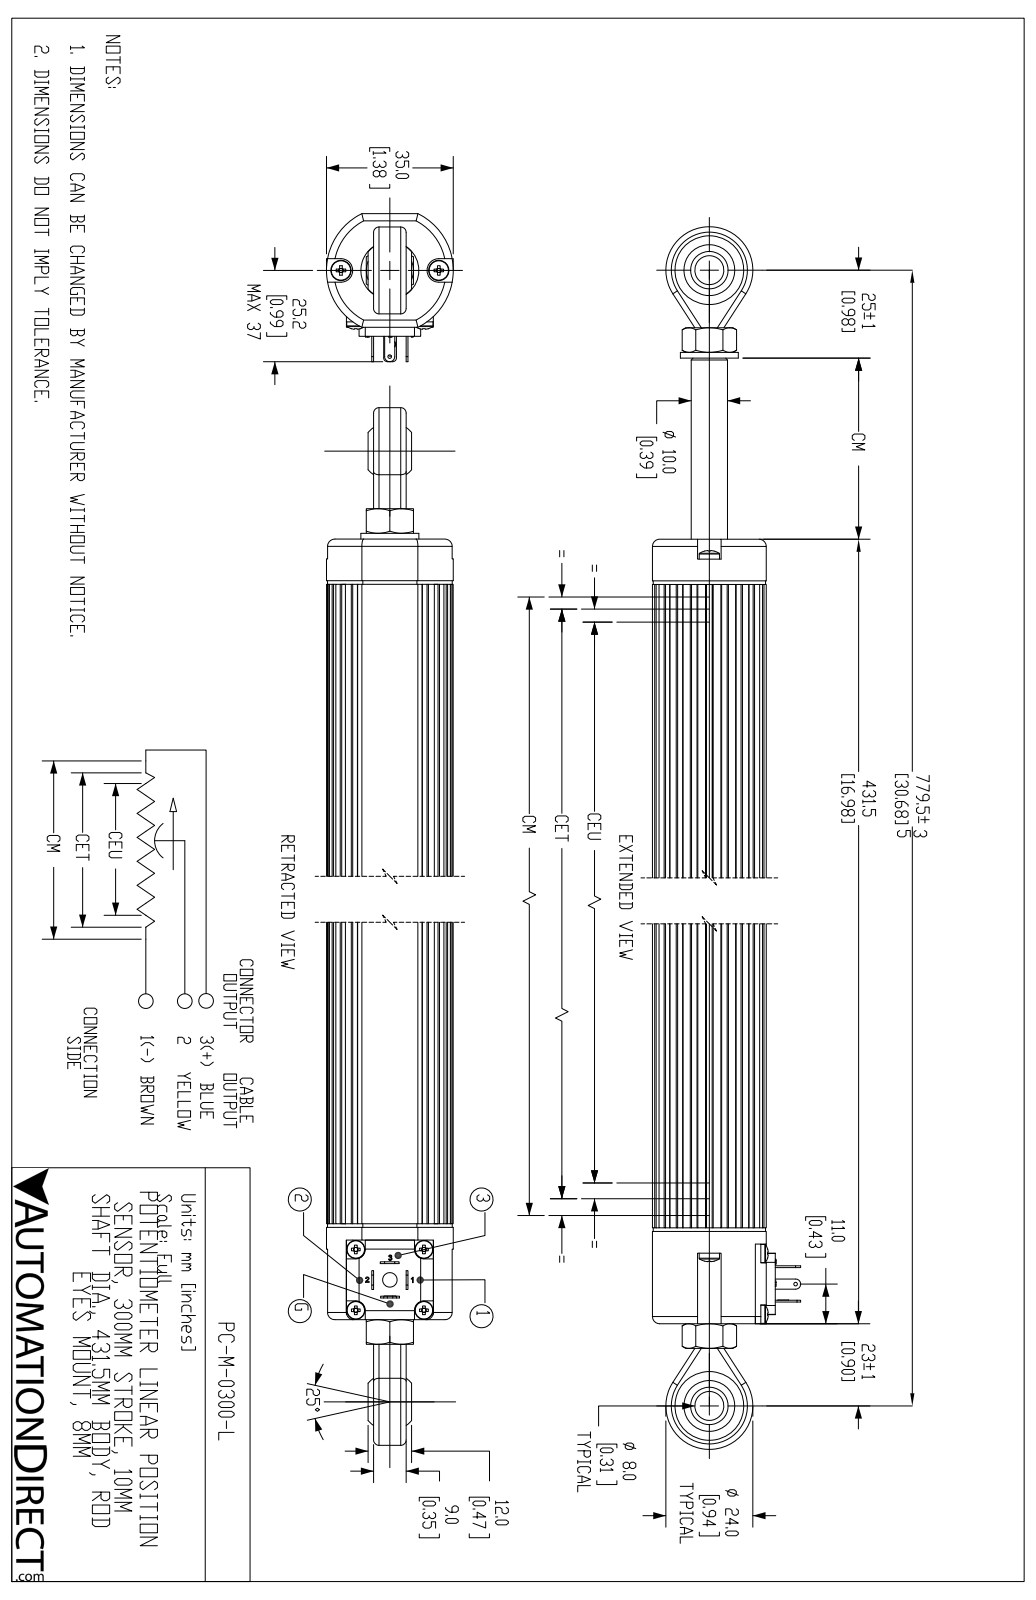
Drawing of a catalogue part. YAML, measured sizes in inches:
part_name: "PC-M-0300-L"
step_written_by: "SolidWorks 2019 (AUTOMOTIVE_DESIGN)"
units: inches
bodies: {solids: 26, faces: 1441, planar: 437, cylindrical: 366, other: 638}
overall_size: [20.025, 1.61, 1.378]
volume: 26.44
surface_area: 140.1
round_holes:
  - {diameter: 0.087, count: 4}
  - {diameter: 0.102, count: 4}
  - {diameter: 0.039, count: 3}
  - {diameter: 0.108, count: 2}
  - {diameter: 0.138, count: 2}
  - {diameter: 0.315, count: 2}
  - {diameter: 0.748, count: 2}
  - {diameter: 0.114, count: 1}
  - {diameter: 0.157, count: 1}
  - {diameter: 0.268, count: 1}
  - {diameter: 0.331, count: 1}
  - {diameter: 0.512, count: 1}
round_bosses_or_shafts:
  - {diameter: 0.197, count: 4}
  - {diameter: 0.098, count: 4}
  - {diameter: 0.118, count: 3}
  - {diameter: 0.22, count: 2}
  - {diameter: 0.63, count: 1}
  - {diameter: 0.394, count: 1}
  - {diameter: 0.39, count: 1}
  - {diameter: 0.315, count: 1}
partial_cylinders:
  - {radius: 0.059, count: 8}
  - {radius: 0.039, count: 5}
  - {radius: 0.079, count: 5}
  - {radius: 0.102, count: 4}
  - {radius: 0.118, count: 4}
  - {radius: 0.055, count: 2}
  - {radius: 0.128, count: 2}
  - {radius: 0.472, count: 2}
face_to_face_distances: [1.236, 0.039, 15.492, 0.913, 15.453, 0.913, 15.531, 0.118, 1.118, 16.535]
hole_center_spacings: [0.496, 0.531, 0.661, 0.74, 0.993, 0.024, 0.11, 0.134]
